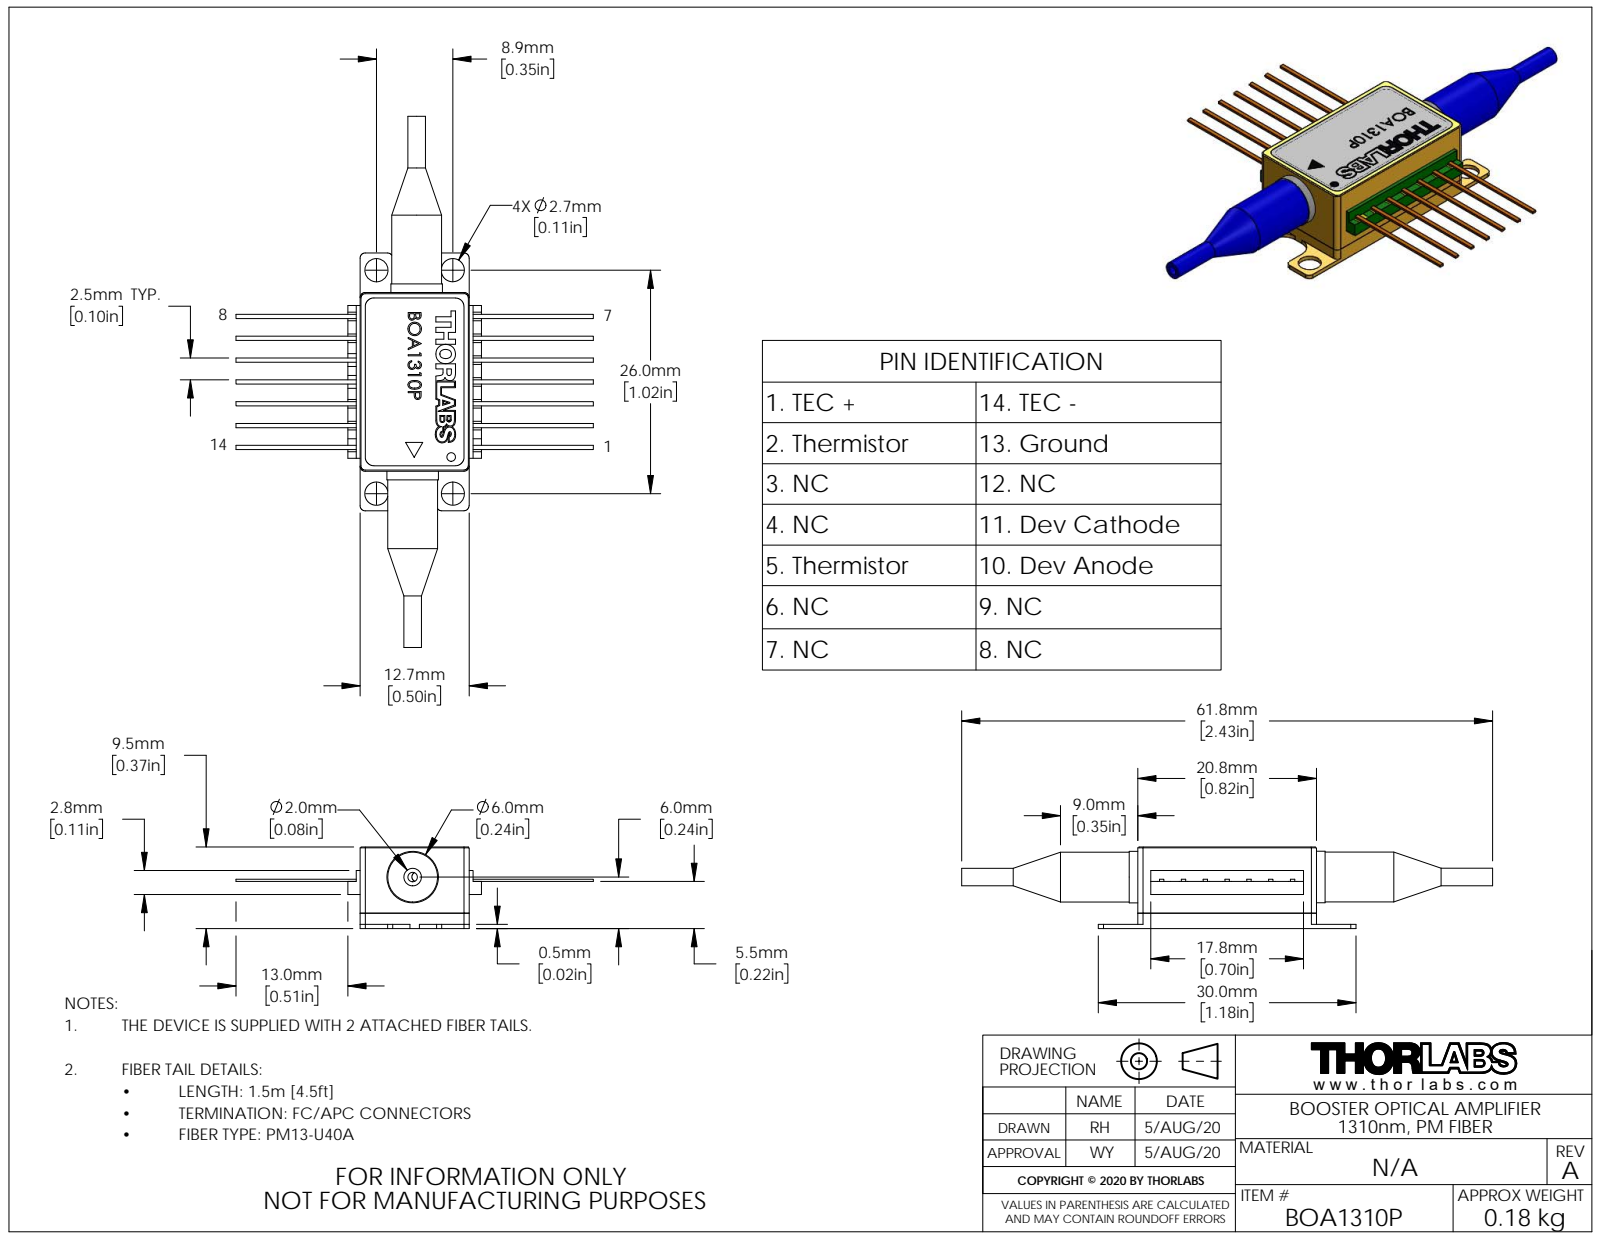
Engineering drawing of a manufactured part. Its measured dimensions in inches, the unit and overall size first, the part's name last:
Units: inches
Overall size (bounding box): 2.433 × 1.638 × 0.374
Round holes (diameter × count): ⌀0.106 ×4, ⌀0.043 ×2, ⌀0.039 ×1
Round bosses / shafts (diameter × count): ⌀0.236 ×2, ⌀0.228 ×2, ⌀0.08 ×2
Partial cylindrical surfaces — rounded edges, fillets, slot ends (radius × count): R0.024 ×12, R0.02 ×4, R0.079 ×4, R0.039 ×1
Main face-to-face distances: 0.374, 0.5, 0.071, 0.303, 0.156, 0.085, 0.217, 0.06, 0.146, 0.217
Hole centre spacings: 0.35, 1.024, 1.082, 0.019, 0.168, 0.382, 0.856, 0.922
Bodies: 0 solids, 349 faces (250 planar, 51 cylindrical, 48 other)
Part name (STEP PRODUCT): QTN042299-E0W
STEP written by: SolidWorks 2018 (AUTOMOTIVE_DESIGN)
